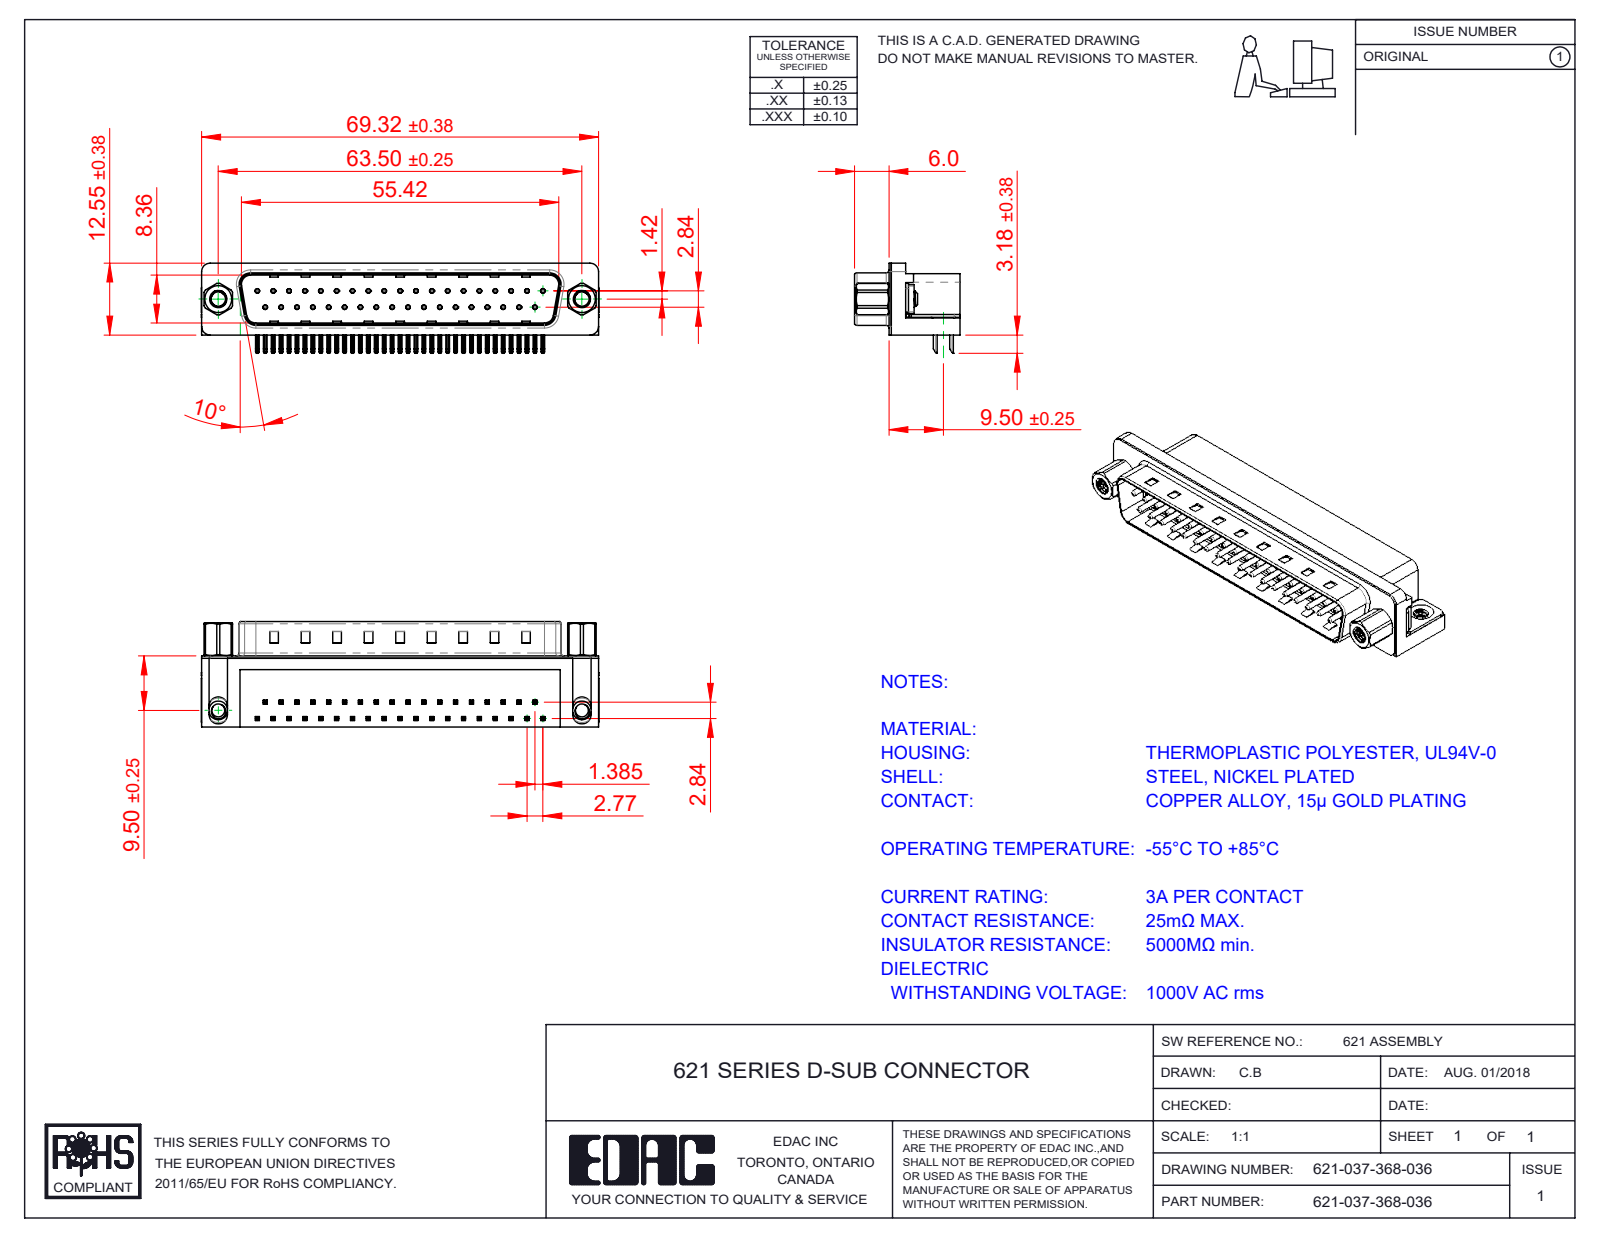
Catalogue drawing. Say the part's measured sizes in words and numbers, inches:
The part is named "621 Shell_37 Socket; 621 Housing_37 Socket; 621 M3 Hex Standoff 5; 621-037-368-036 (+4 more)". Its 3-D file was written by "SolidWorks 2016 (CONFIG_CONTROL_DESIGN)". It is 45 solids with 3387 faces: 2067 planar, 1019 cylindrical and 301 other. Overall it measures 2.732 by 0.724 by 0.64 inches. Its volume is 0.541 cubic inches and its surface area 16.48 square inches. Round holes: 37 of diameter 0.014, 37 of diameter 0.031, 2 of diameter 0.098, 2 of diameter 0.157, 2 of diameter 0.189, 2 of diameter 0.197. Round bosses or shafts: 37 of diameter 0.03, 2 of diameter 0.193, 2 of diameter 0.187, 2 of diameter 0.154, 2 of diameter 0.118. Partial cylindrical surfaces (rounded edges, fillets, slot ends): 156 of radius 0.01, 74 of radius 0.005, 16 of radius 0.039, 14 of radius 0.02, 8 of radius 0.063, 7 of radius 0.059, 4 of radius 0.013, 4 of radius 0.035. The main face-to-face distances are 0.016, 0.472, 0.407, 0.345, 0.067, 0.083, 0.412, 0.428, 0.354, 0.488. The hole center spacings are 0.124, 0.109, 0.218, 0.327, 0.436, 0.545, 0.763, 0.872.
